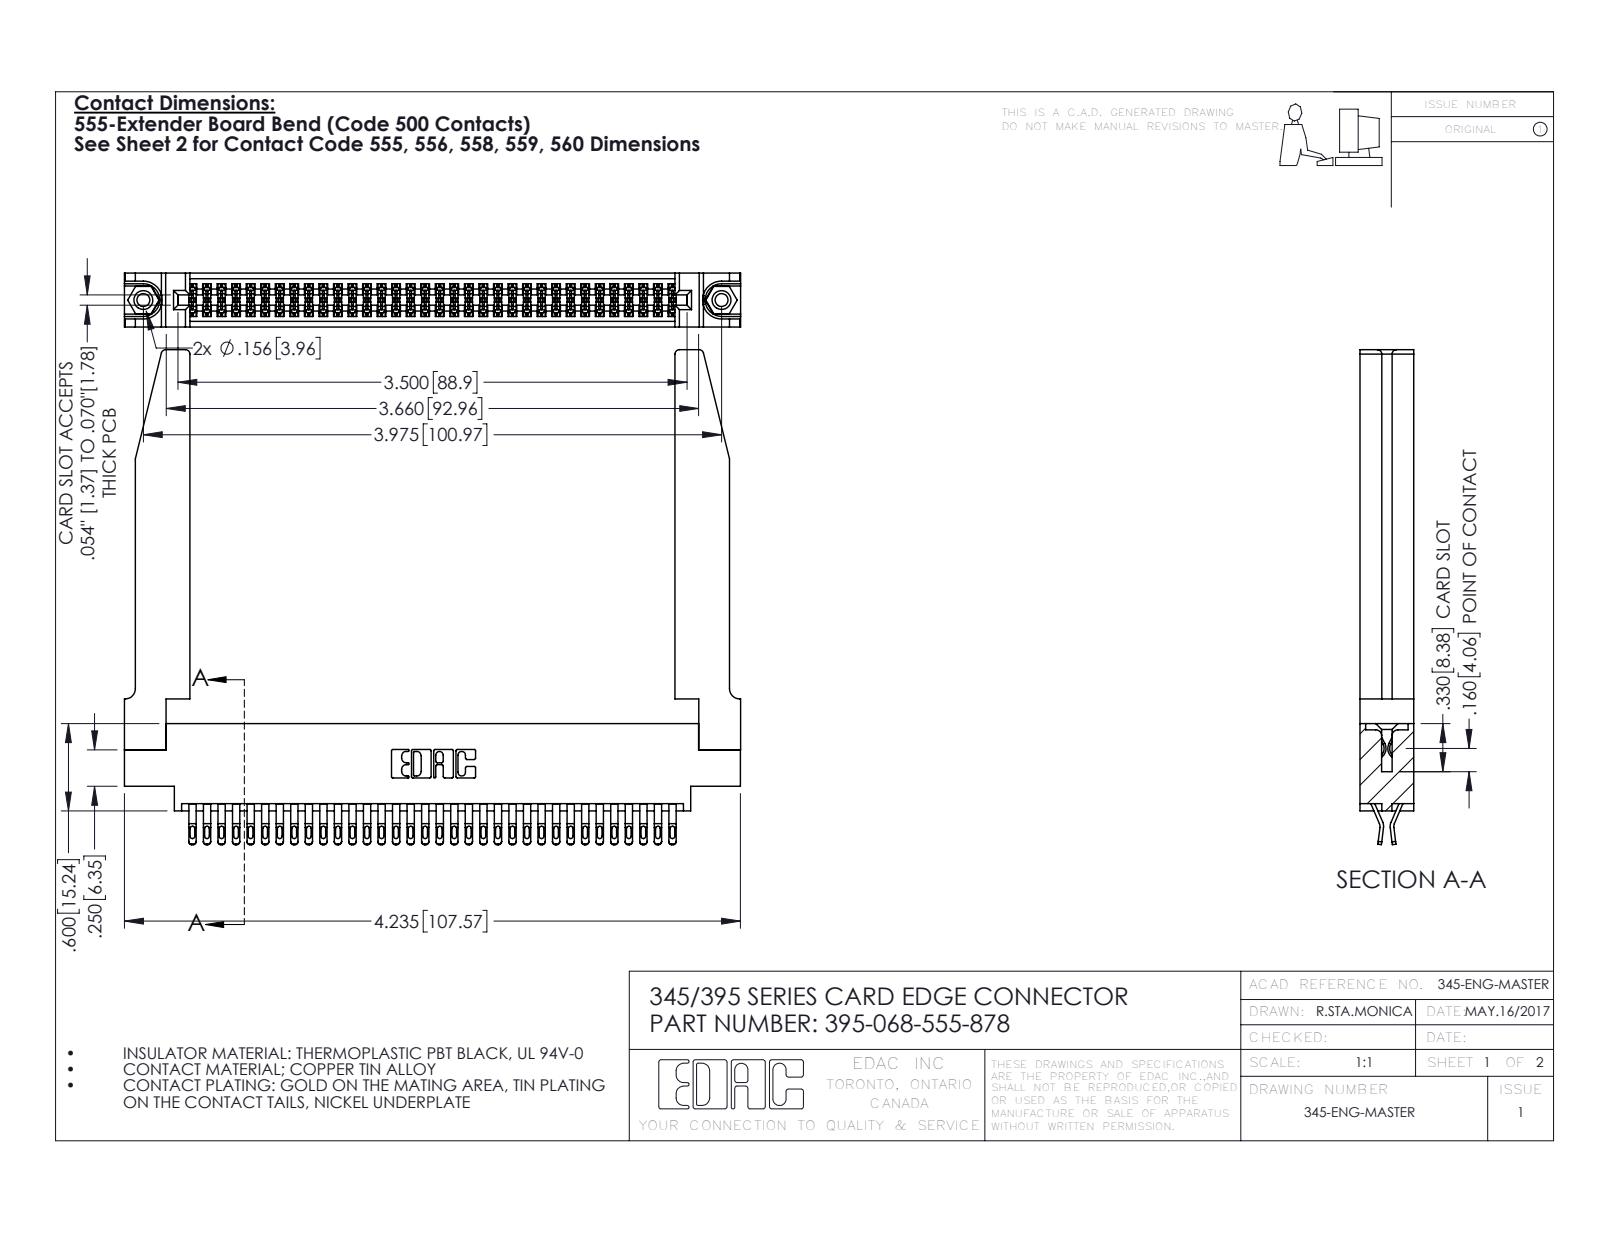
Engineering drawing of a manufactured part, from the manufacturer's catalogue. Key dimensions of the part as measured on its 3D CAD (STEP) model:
Part name (STEP PRODUCT): 345-292-001_555 Tail; 345-250-001_345-250-001-102; 345 Part_0.170 Offset - 0.156 Dia-TH; 395-068-555-878 (+1 more)
STEP written by: SolidWorks 2016 (CONFIG_CONTROL_DESIGN)
Units: inches
Bodies: 73 solids, 4172 faces (2334 planar, 1786 cylindrical, 52 other)
Overall size (bounding box): 4.236 × 3.402 × 0.37
Volume: 1.113 in³ · Surface area: 35.61 in²
Round holes (diameter × count): ⌀0.089 ×2, ⌀0.125 ×2, ⌀0.156 ×2, ⌀0.064 ×1
Round bosses / shafts (diameter × count): ⌀0.155 ×2
Partial cylindrical surfaces — rounded edges, fillets, slot ends (radius × count): R0.016 ×170, R0.02 ×136, R0.006 ×102, R0.01 ×22, R0.03 ×8, R0.007 ×6, R0.031 ×6, R0.026 ×3
Main face-to-face distances: 0.37, 0.072, 0.298, 0.025, 0.2, 0.098, 0.272, 0.225, 0.15, 0.148
Hole centre spacings: 0.27, 3.74, 3.975
